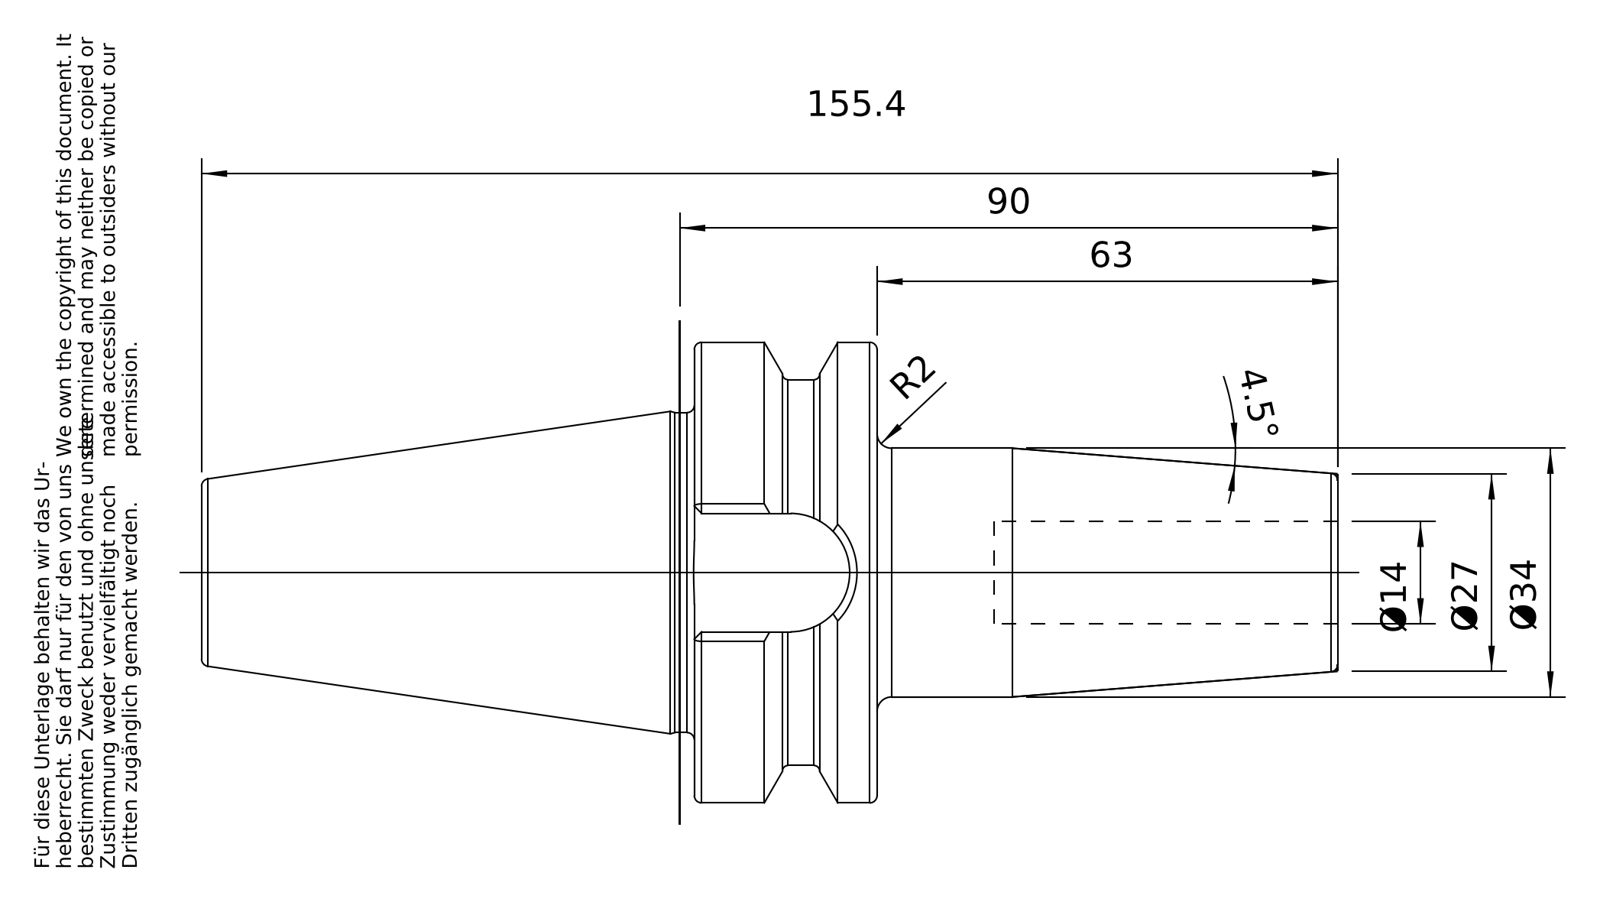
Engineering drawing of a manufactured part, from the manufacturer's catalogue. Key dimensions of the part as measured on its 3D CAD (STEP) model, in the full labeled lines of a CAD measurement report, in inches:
Part name (STEP PRODUCT): 40-640-14
STEP written by: PRO/ENGINEER BY PARAMETRIC TECHNOLOGY CORPORATION, 2010430 (CONFIG_CONTROL_DESIGN)
Units: inches
Bodies: 1 solid, 96 faces (26 planar, 22 cylindrical, 48 other)
Overall size (bounding box): 6.118 × 2.48 × 2.48
Volume: 10.28 in³ · Surface area: 46.03 in²
Round holes (diameter × count): ⌀0.545 ×1, ⌀0.551 ×1, ⌀0.67 ×1, ⌀0.689 ×1
Round bosses / shafts (diameter × count): ⌀2.48 ×1, ⌀2.077 ×1, ⌀1.722 ×1, ⌀1.339 ×1, ⌀0.63 ×1
Partial cylindrical surfaces — rounded edges, fillets, slot ends (radius × count): R0.319 ×1
Main face-to-face distances: 0.984, 3.465, 2.48, 1.768, 1.614, 0.63, 1.85, 0.638, 2.654, 3.638
